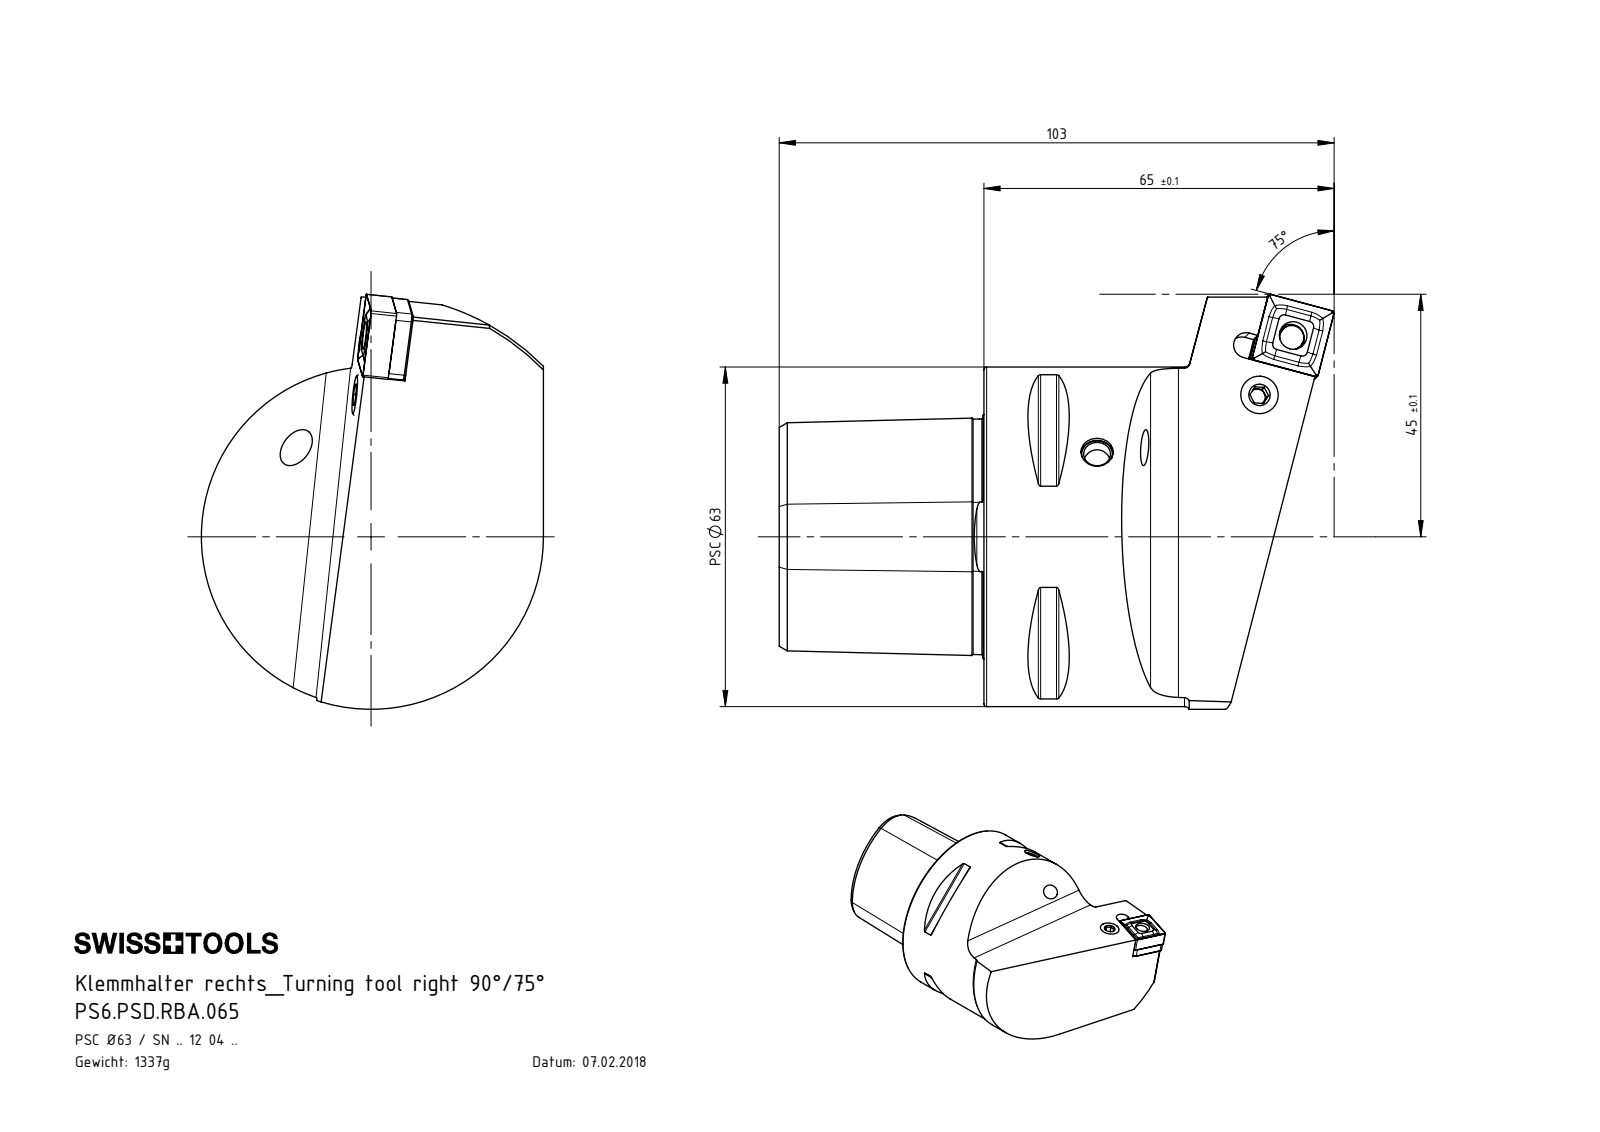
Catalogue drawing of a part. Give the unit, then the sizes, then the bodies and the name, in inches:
Units: inches
Overall size (bounding box): 4.055 × 3.031 × 2.5
Round holes (diameter × count): ⌀0.197 ×2, ⌀0.157 ×1, ⌀0.203 ×1, ⌀0.252 ×1, ⌀0.276 ×1, ⌀0.319 ×1, ⌀0.331 ×1, ⌀0.709 ×1, ⌀1.102 ×1, ⌀1.26 ×1
Round bosses / shafts (diameter × count): ⌀2.48 ×1, ⌀0.315 ×1, ⌀0.311 ×1, ⌀0.252 ×1, ⌀0.236 ×1, ⌀0.177 ×1, ⌀0.14 ×1
Partial cylindrical surfaces — rounded edges, fillets, slot ends (radius × count): R0.02 ×8, R0.016 ×4, R0.047 ×4, R0.098 ×2, R0.236 ×2, R0.087 ×1, R0.093 ×1, R0.11 ×1
Main face-to-face distances: 1.496, 0.98, 0.481, 1.063, 0.433, 0.125, 2.197, 0.5, 0.176, 1.488
Hole centre spacings: 0.504, 1.083
Volume: 10.36 in³ · Surface area: 48.48 in²
Bodies: 8 solids, 339 faces (89 planar, 83 cylindrical, 167 other)
Part name (STEP PRODUCT): PS6.PSD.RBA.065; KVT_MB_600_060; WCD-ER3.101.000_A; WCD-ER1.101.000 (+4 more)
STEP written by: SolidWorks 2017 (AUTOMOTIVE_DESIGN)
